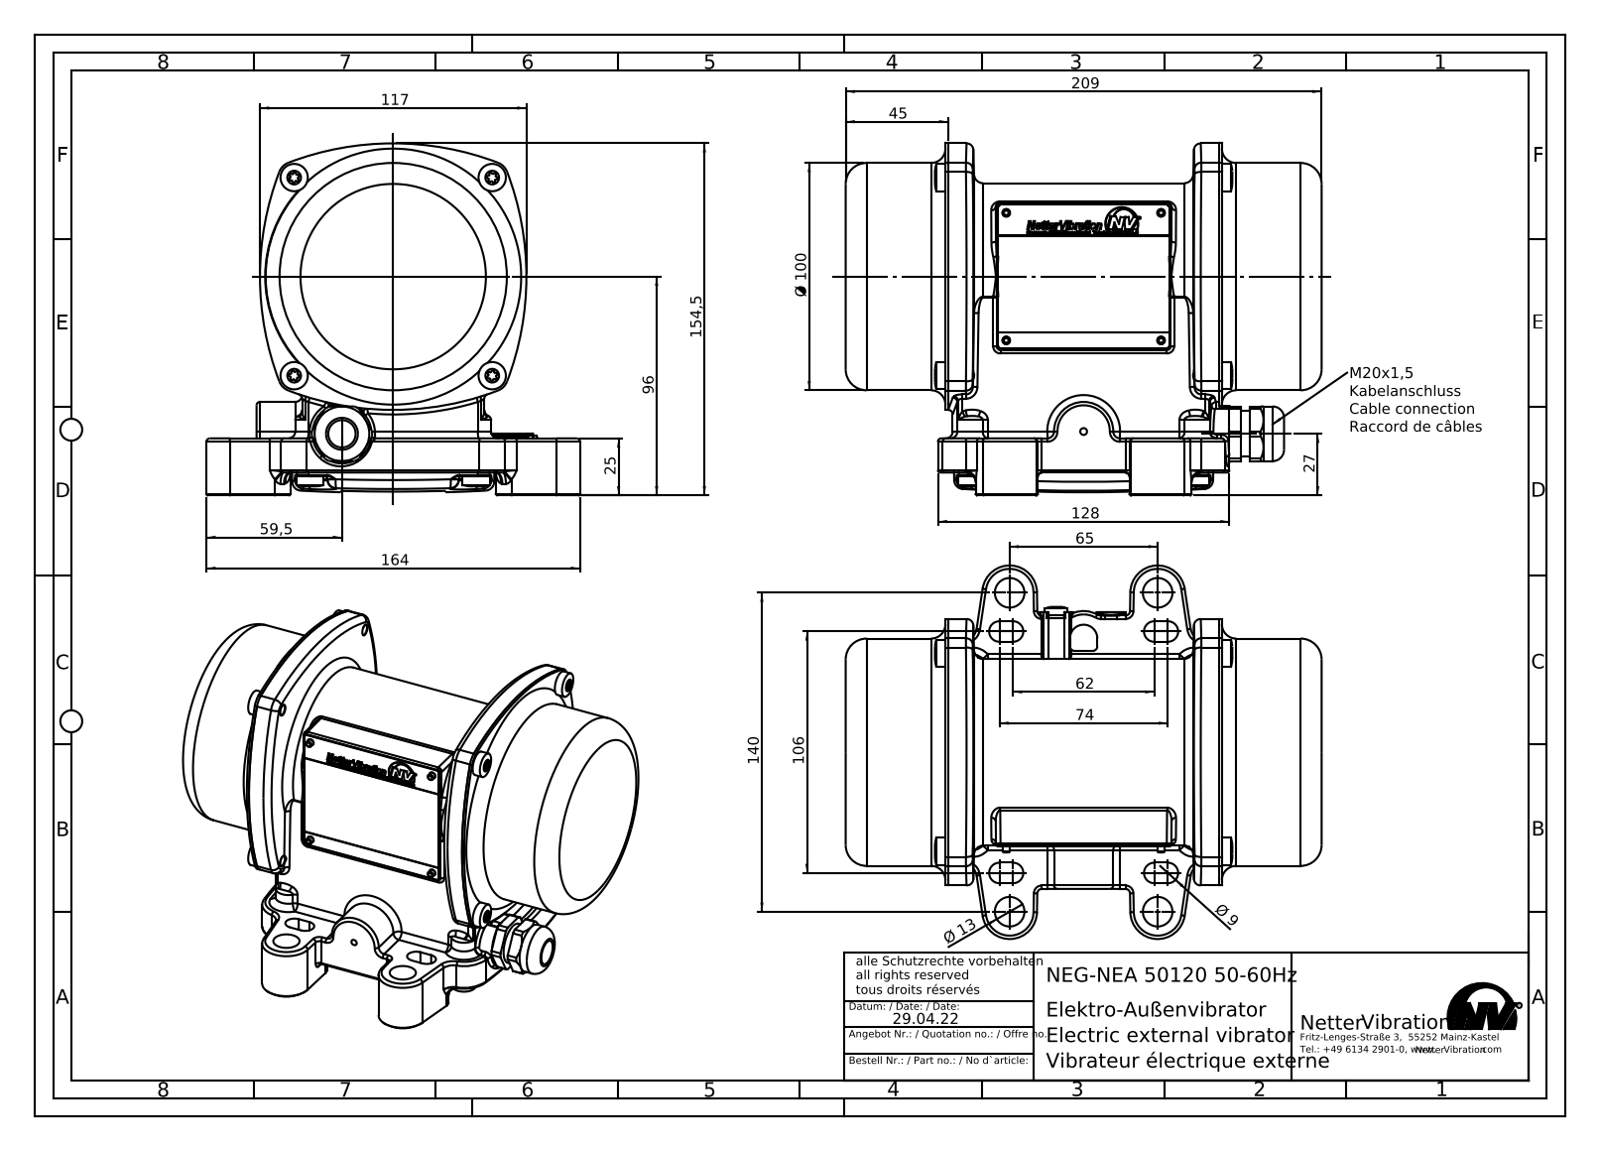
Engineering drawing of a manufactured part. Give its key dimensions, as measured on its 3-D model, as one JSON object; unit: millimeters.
{"part_name": "NEA-NEG 50120-50-60Hz", "step_written_by": "SolidWorks 2015 (AUTOMOTIVE_DESIGN)", "units": "millimeters", "bodies": {"solids": 20, "faces": 3072, "planar": 763, "cylindrical": 766, "other": 1543}, "overall_size": [209, 164, 154.5], "volume_mm3": 675916, "surface_area_mm2": 319951, "round_holes": [[3.4, 4], [7, 4], [3.3, 1], [10.5, 1], [11.5, 1], [12, 1], [13, 1], [14.5, 1], [18.5, 1], [84, 1], [97.4, 1]], "round_bosses_or_shafts": [[12, 8], [6, 8], [99.8, 1], [24, 1], [20, 1], [13, 1], [10, 1], [5, 1]], "partial_cylinders_radius": [[1.5, 59], [0.5, 55], [0.2, 41], [2, 28], [1, 26], [3, 16], [6, 15], [1.75, 9]], "face_to_face_distances": [1.2, 43.8, 164, 207.8, 45, 162.8, 0.5, 81, 209, 206.6], "hole_center_spacings": [61.5, 86.98, 56, 68, 88.09, 123.01, 24.25, 33.04]}
